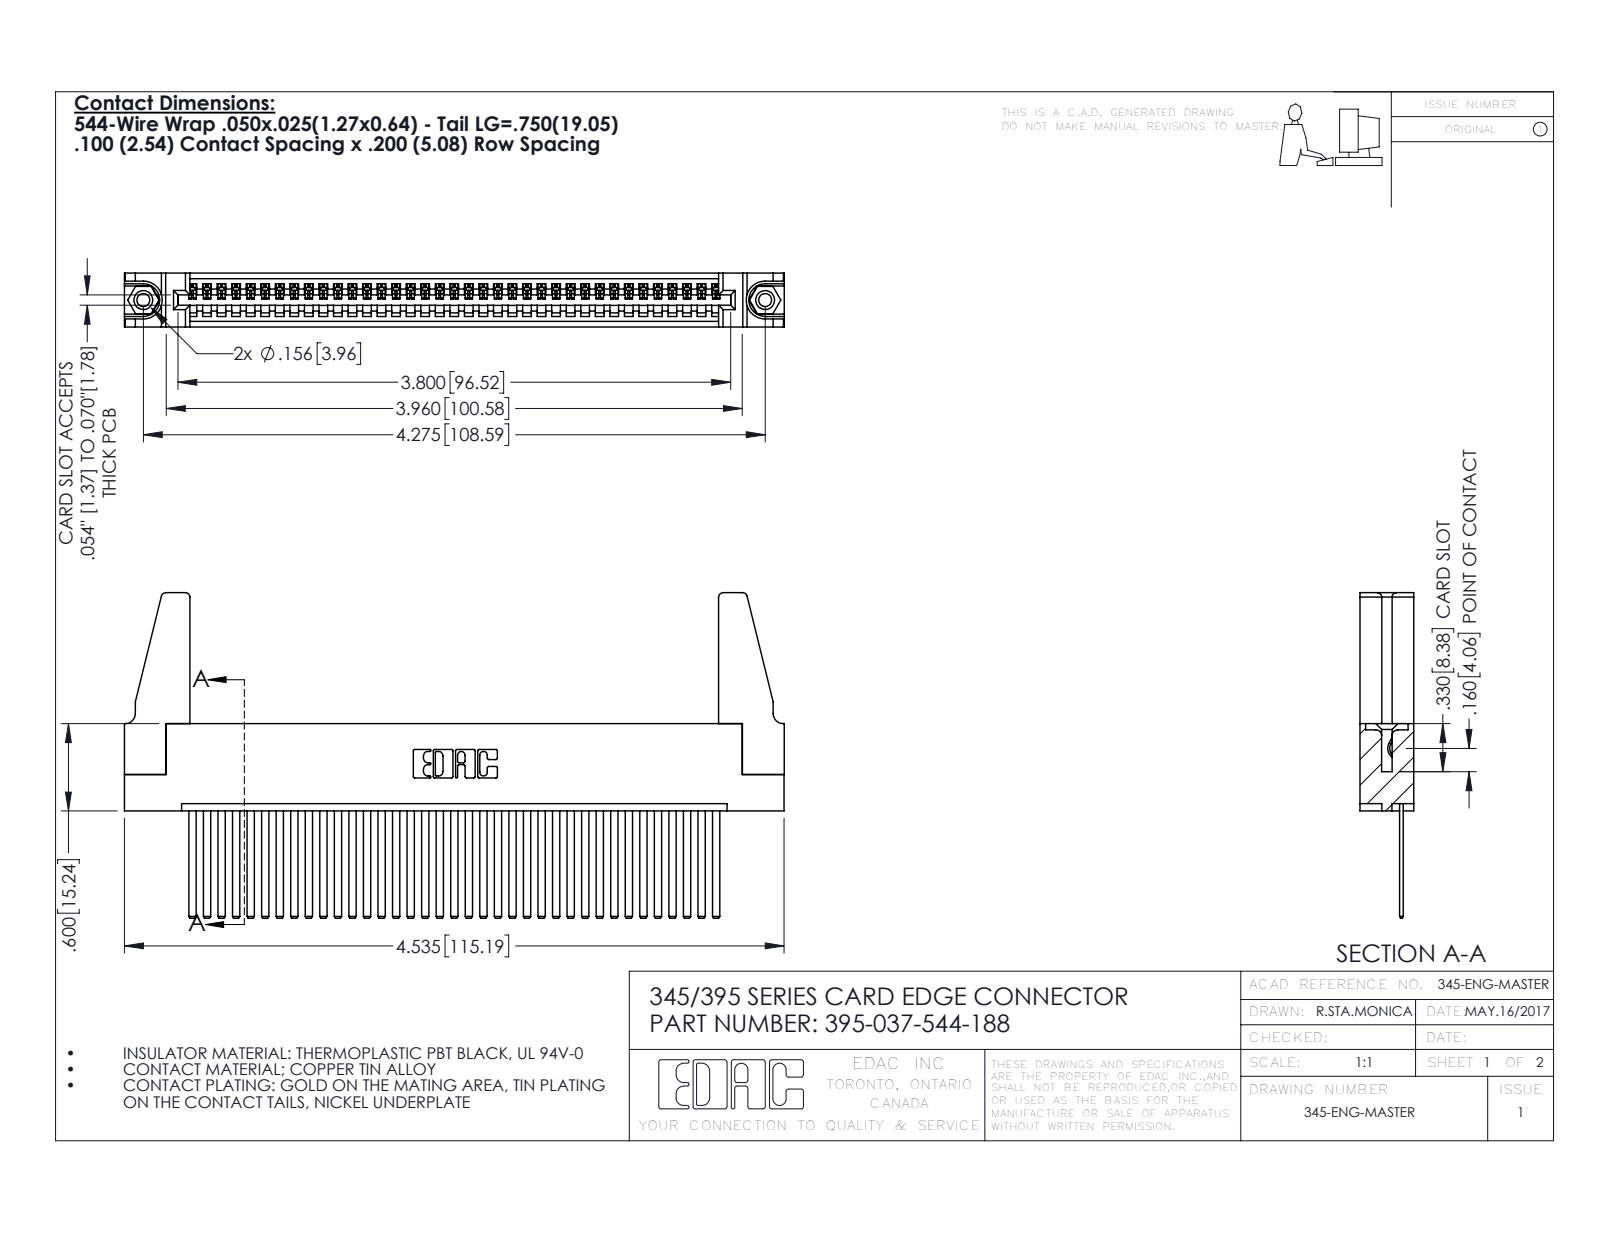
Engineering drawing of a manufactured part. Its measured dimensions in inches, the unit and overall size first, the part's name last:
Units: inches
Overall size (bounding box): 4.536 × 2.237 × 0.37
Round holes (diameter × count): ⌀0.089 ×2, ⌀0.125 ×2, ⌀0.156 ×2, ⌀0.064 ×1
Round bosses / shafts (diameter × count): ⌀0.155 ×2
Partial cylindrical surfaces — rounded edges, fillets, slot ends (radius × count): R0.006 ×74, R0.01 ×22, R0.03 ×8, R0.007 ×6, R0.031 ×6, R0.026 ×3, R0.031 ×2, R0.04 ×2
Main face-to-face distances: 0.072, 0.298, 0.098, 0.272, 0.025, 0.37, 0.2, 0.225, 0.149, 0.072
Hole centre spacings: 0.27, 4.039, 4.275
Volume: 0.89 in³ · Surface area: 30.08 in²
Bodies: 42 solids, 2174 faces (1484 planar, 674 cylindrical, 16 other)
Part name (STEP PRODUCT): 395-037-544-188; 345-292-001_345-293-144; 345-250-001_345-250-001-102; 345 Part_Flush Mounting Lugs - 0.156 Dia-TH (+1 more)
STEP written by: SolidWorks 2016 (CONFIG_CONTROL_DESIGN)
